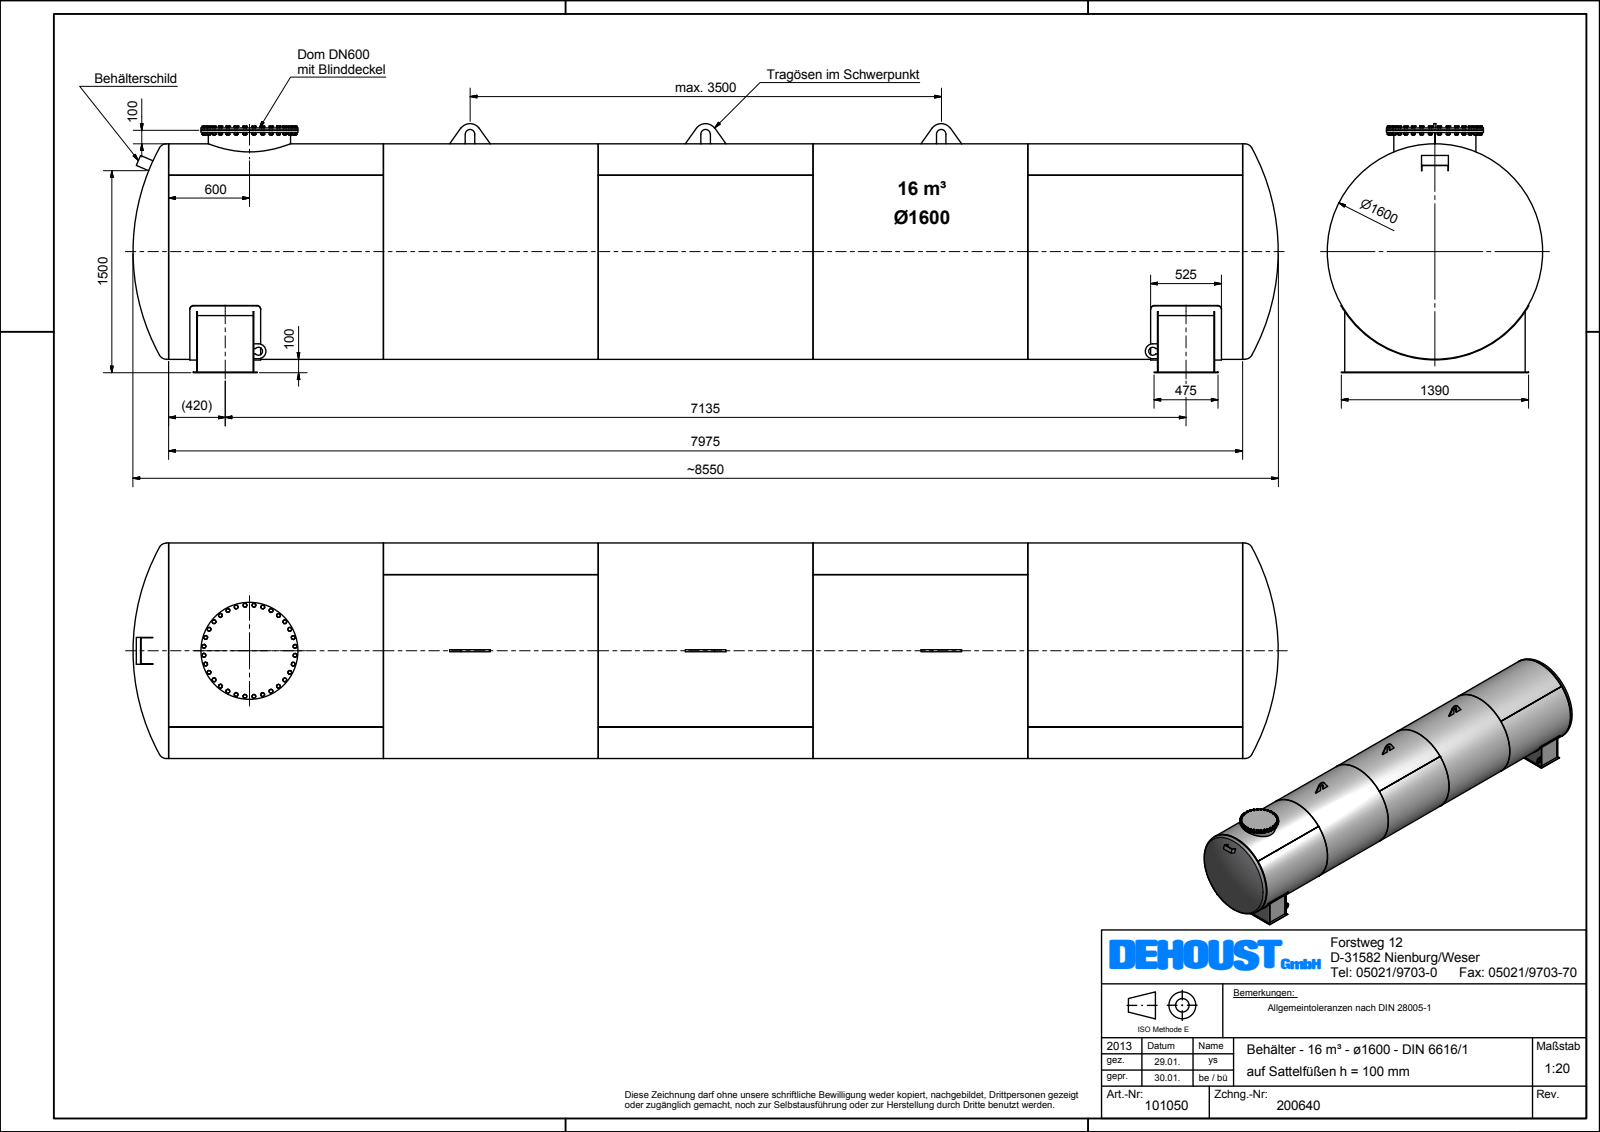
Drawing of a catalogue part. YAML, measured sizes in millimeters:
part_name: "Beh\\S\\dlter_6616_E_1600_016_100_KV"
step_written_by: "Autodesk Inventor 2012 (AUTOMOTIVE_DESIGN)"
units: millimeters
bodies: {solids: 5, faces: 1151, planar: 688, cylindrical: 171, other: 292}
overall_size: [8505.51, 1850, 1600]
volume: 886300000
surface_area: 96710000
round_holes:
  - {diameter: 598, count: 1}
  - {diameter: 1590, count: 1}
round_bosses_or_shafts:
  - {diameter: 24.8, count: 32}
  - {diameter: 18, count: 32}
  - {diameter: 16.65, count: 32}
  - {diameter: 1600, count: 1}
  - {diameter: 720, count: 1}
  - {diameter: 660, count: 1}
  - {diameter: 610, count: 1}
partial_cylinders:
  - {radius: 30, count: 8}
  - {radius: 35, count: 3}
  - {radius: 85, count: 3}
  - {radius: 29.73, count: 2}
  - {radius: 55, count: 2}
  - {radius: 805, count: 1}
face_to_face_distances: [5, 7975, 7135, 420, 1295, 632.5, 207.5, 7767.5, 7342.5, 425]
